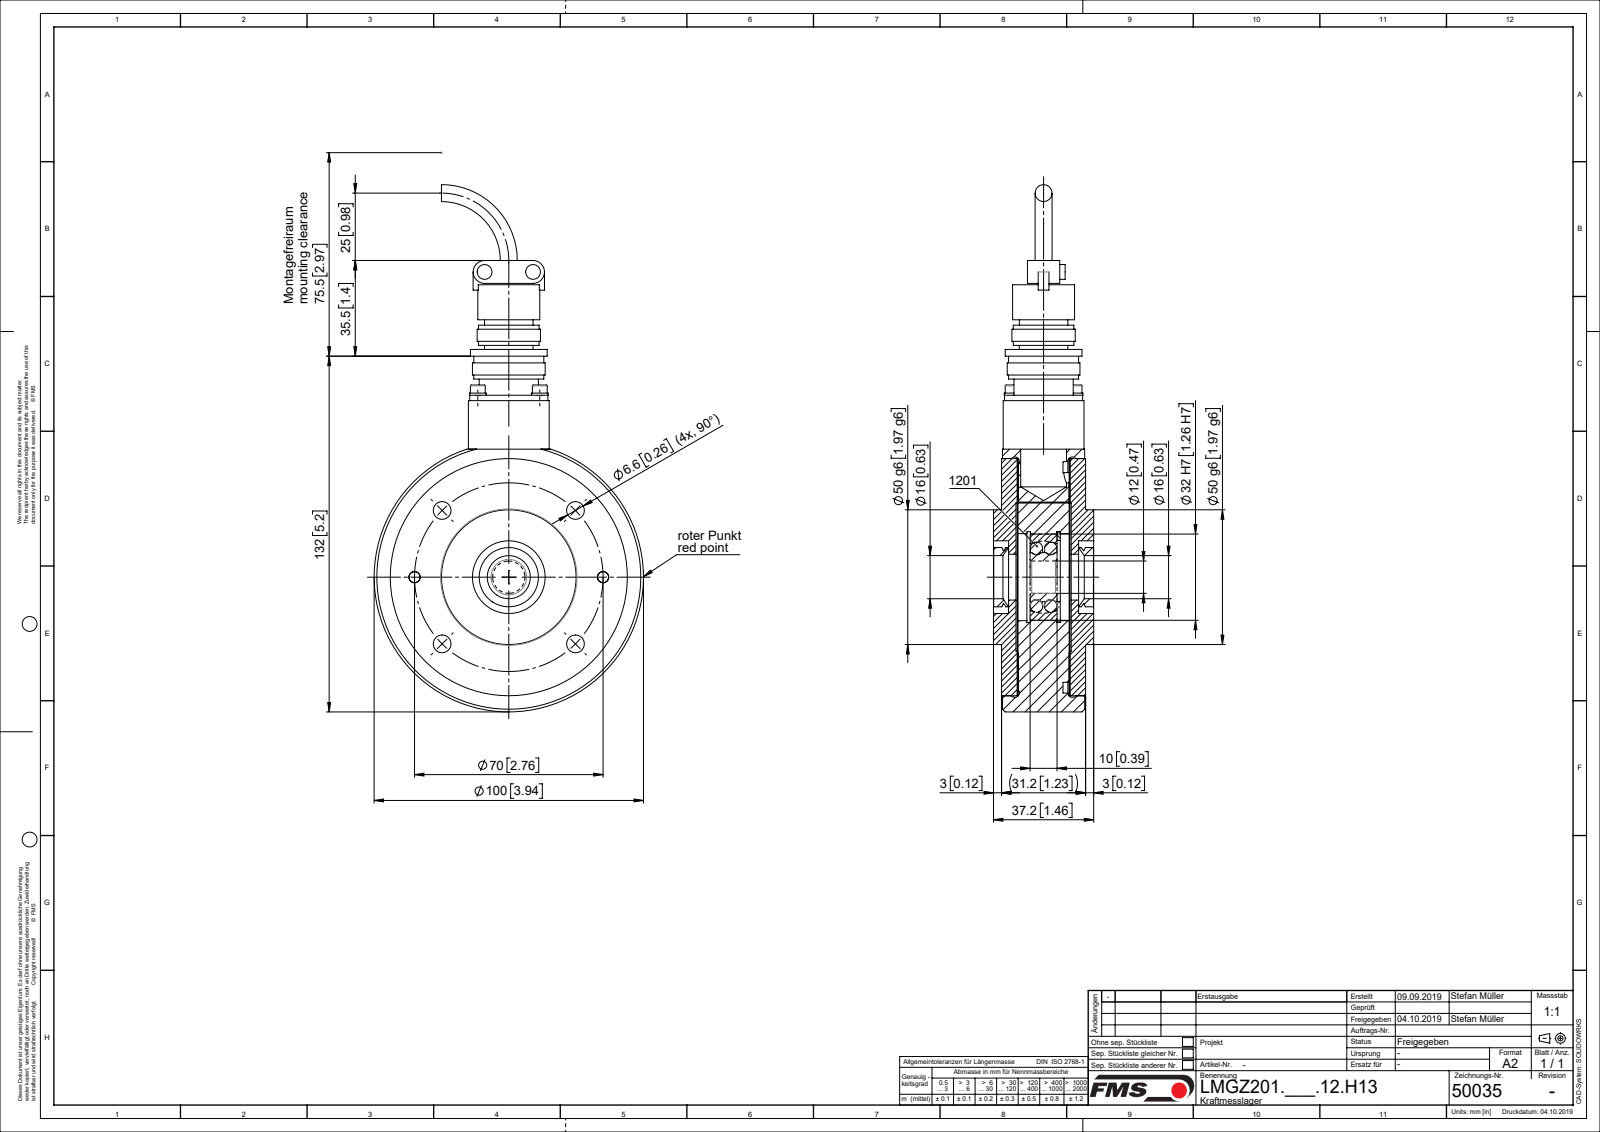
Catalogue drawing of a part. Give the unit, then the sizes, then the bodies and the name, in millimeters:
Units: millimetres
Overall size (bounding box): 195.65 × 100 × 37.2
Round holes (diameter × count): ⌀6.6 ×7, ⌀2.6 ×4, ⌀3.2 ×4, ⌀3.4 ×4, ⌀4 ×2, ⌀5.5 ×2, ⌀10 ×2, ⌀12 ×1, ⌀16 ×1, ⌀17 ×1, ⌀23 ×1, ⌀25.4 ×1
Round bosses / shafts (diameter × count): ⌀5.5 ×6, ⌀6.2 ×4, ⌀3 ×4, ⌀2.5 ×4, ⌀22 ×2, ⌀8 ×2, ⌀5 ×2, ⌀100 ×1
Partial cylindrical surfaces — rounded edges, fillets, slot ends (radius × count): R4.25 ×2
Main face-to-face distances: 19.25, 19, 5.85, 6.1, 25.1, 25.35, 19.5, 20, 5.5, 0.5
Hole centre spacings: 35, 49.5, 49.52, 16.26, 23, 26.79, 64.67, 70
Volume: 265 947 mm³ · Surface area: 97 266 mm²
Bodies: 21 solids, 397 faces (116 planar, 231 cylindrical, 50 other)
Part name (STEP PRODUCT): L50035; L4866604; TEIL1; L48891 (+8 more)
STEP written by: Mechanical Desktop 2007 (CONFIG_CONTROL_DESIGN)
